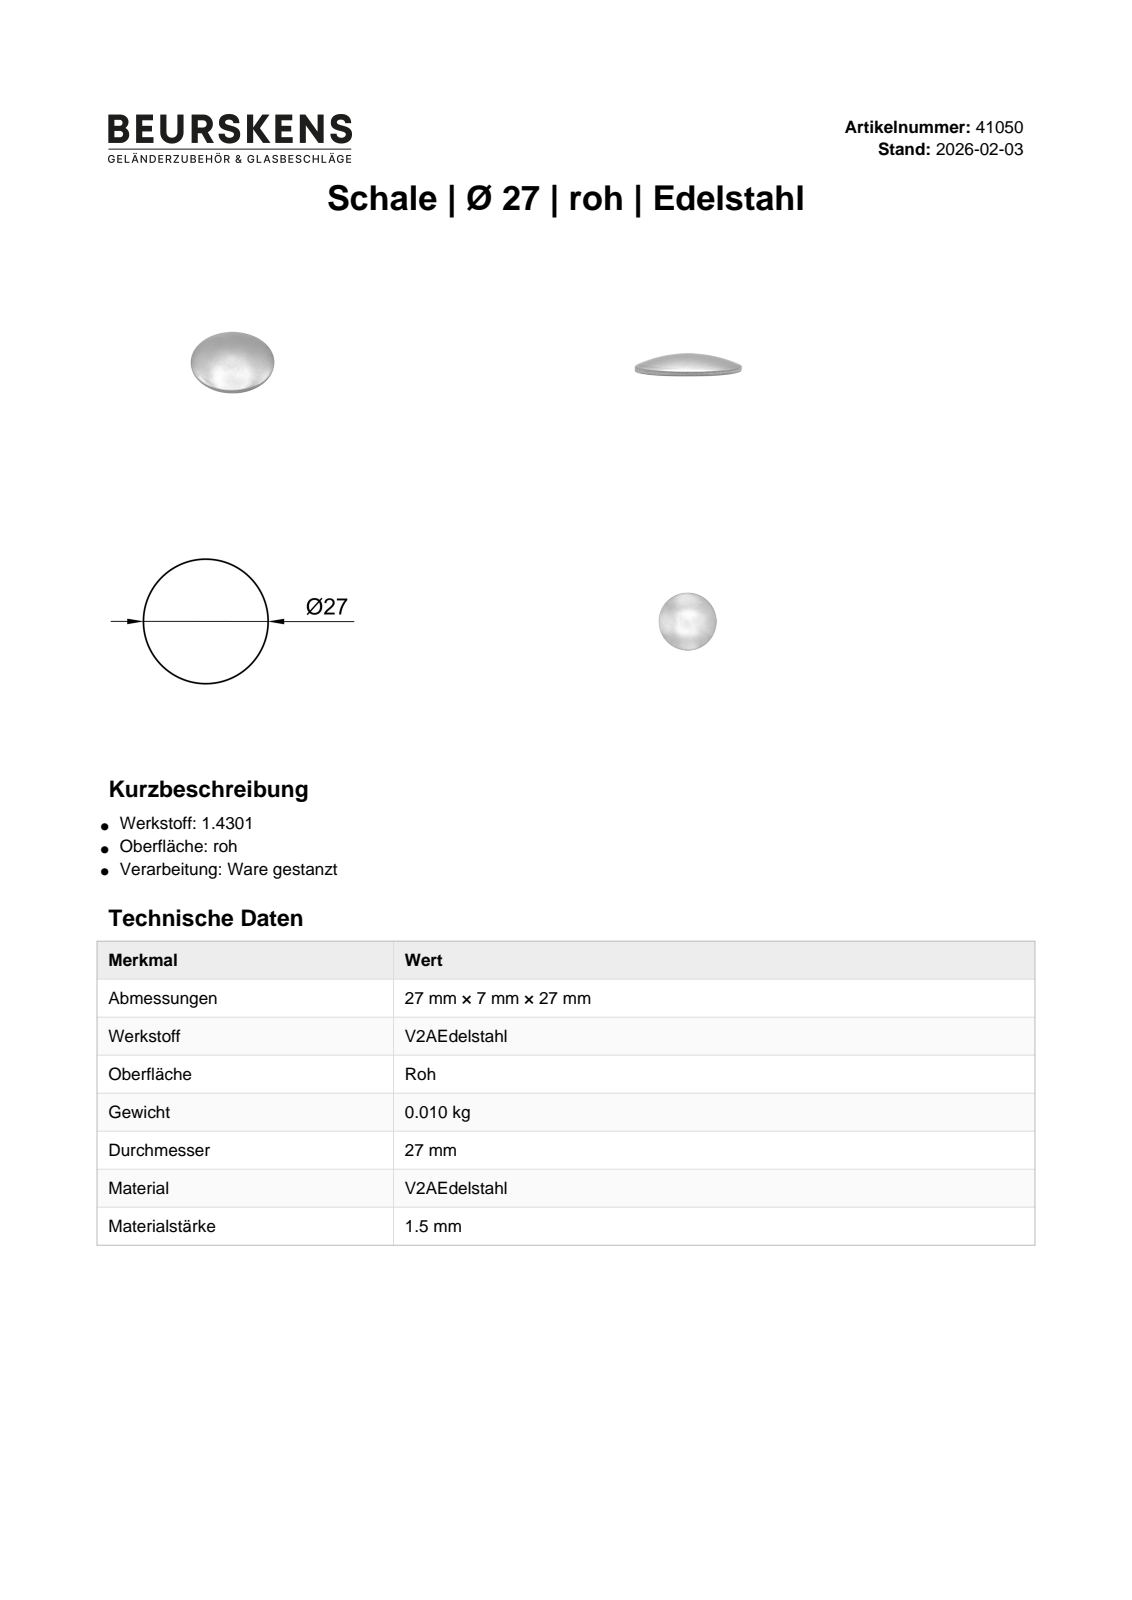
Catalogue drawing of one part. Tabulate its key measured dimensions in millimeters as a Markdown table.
| quantity | value |
| --- | --- |
| part name | 41050 |
| STEP written by | Autodesk Inventor 2022 (AUTOMOTIVE_DESIGN) |
| units | millimeters |
| bodies | 1 solid, 3 faces (1 planar, 0 cylindrical, 2 other) |
| overall size | 27 × 27 × 6 |
| volume | 864 mm³ |
| surface area | 1 322 mm² |
